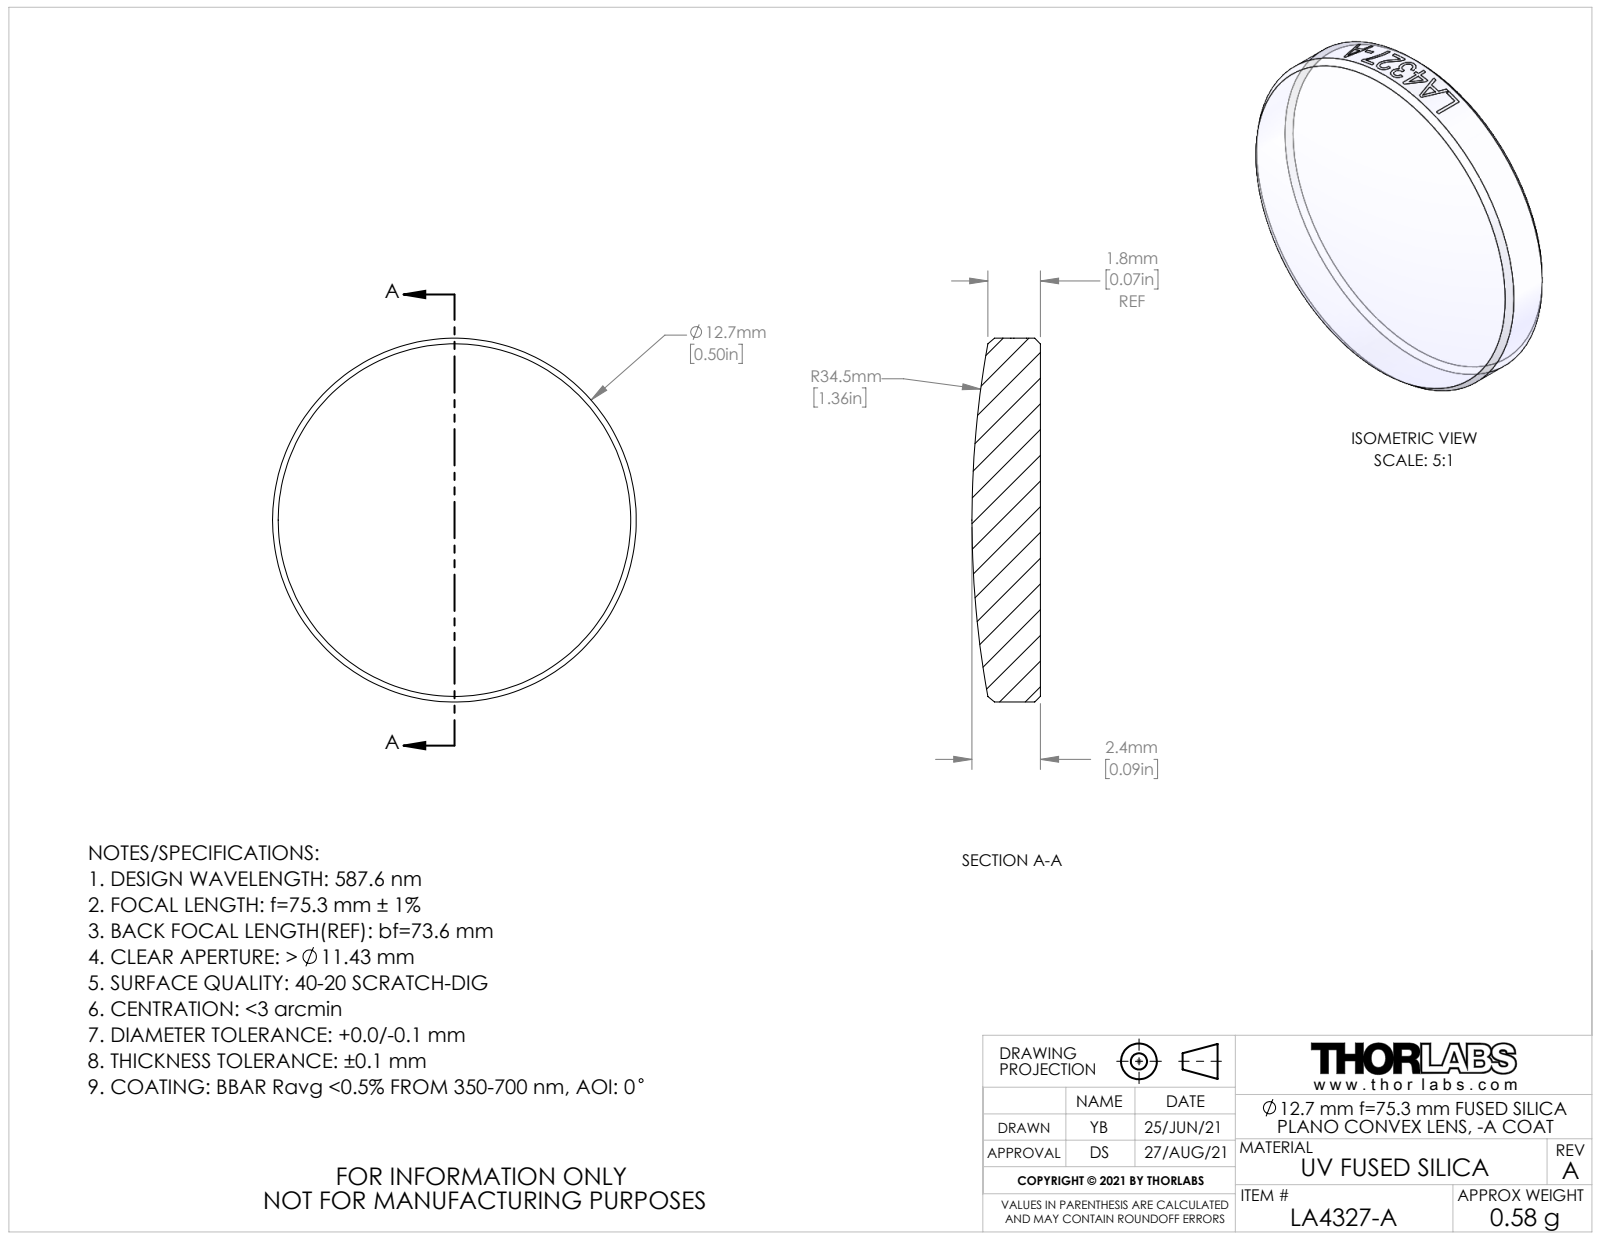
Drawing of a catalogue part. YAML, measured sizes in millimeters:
part_name: "CTN017557; CTN017529-E0W"
step_written_by: "SolidWorks 2018 (AUTOMOTIVE_DESIGN)"
units: millimeters
bodies: {solids: 1, faces: 20, planar: 1, cylindrical: 13, other: 6}
overall_size: [12.7, 12.7, 2.39]
volume: 264
surface_area: 318
round_bosses_or_shafts:
  - {diameter: 12.7, count: 1}
